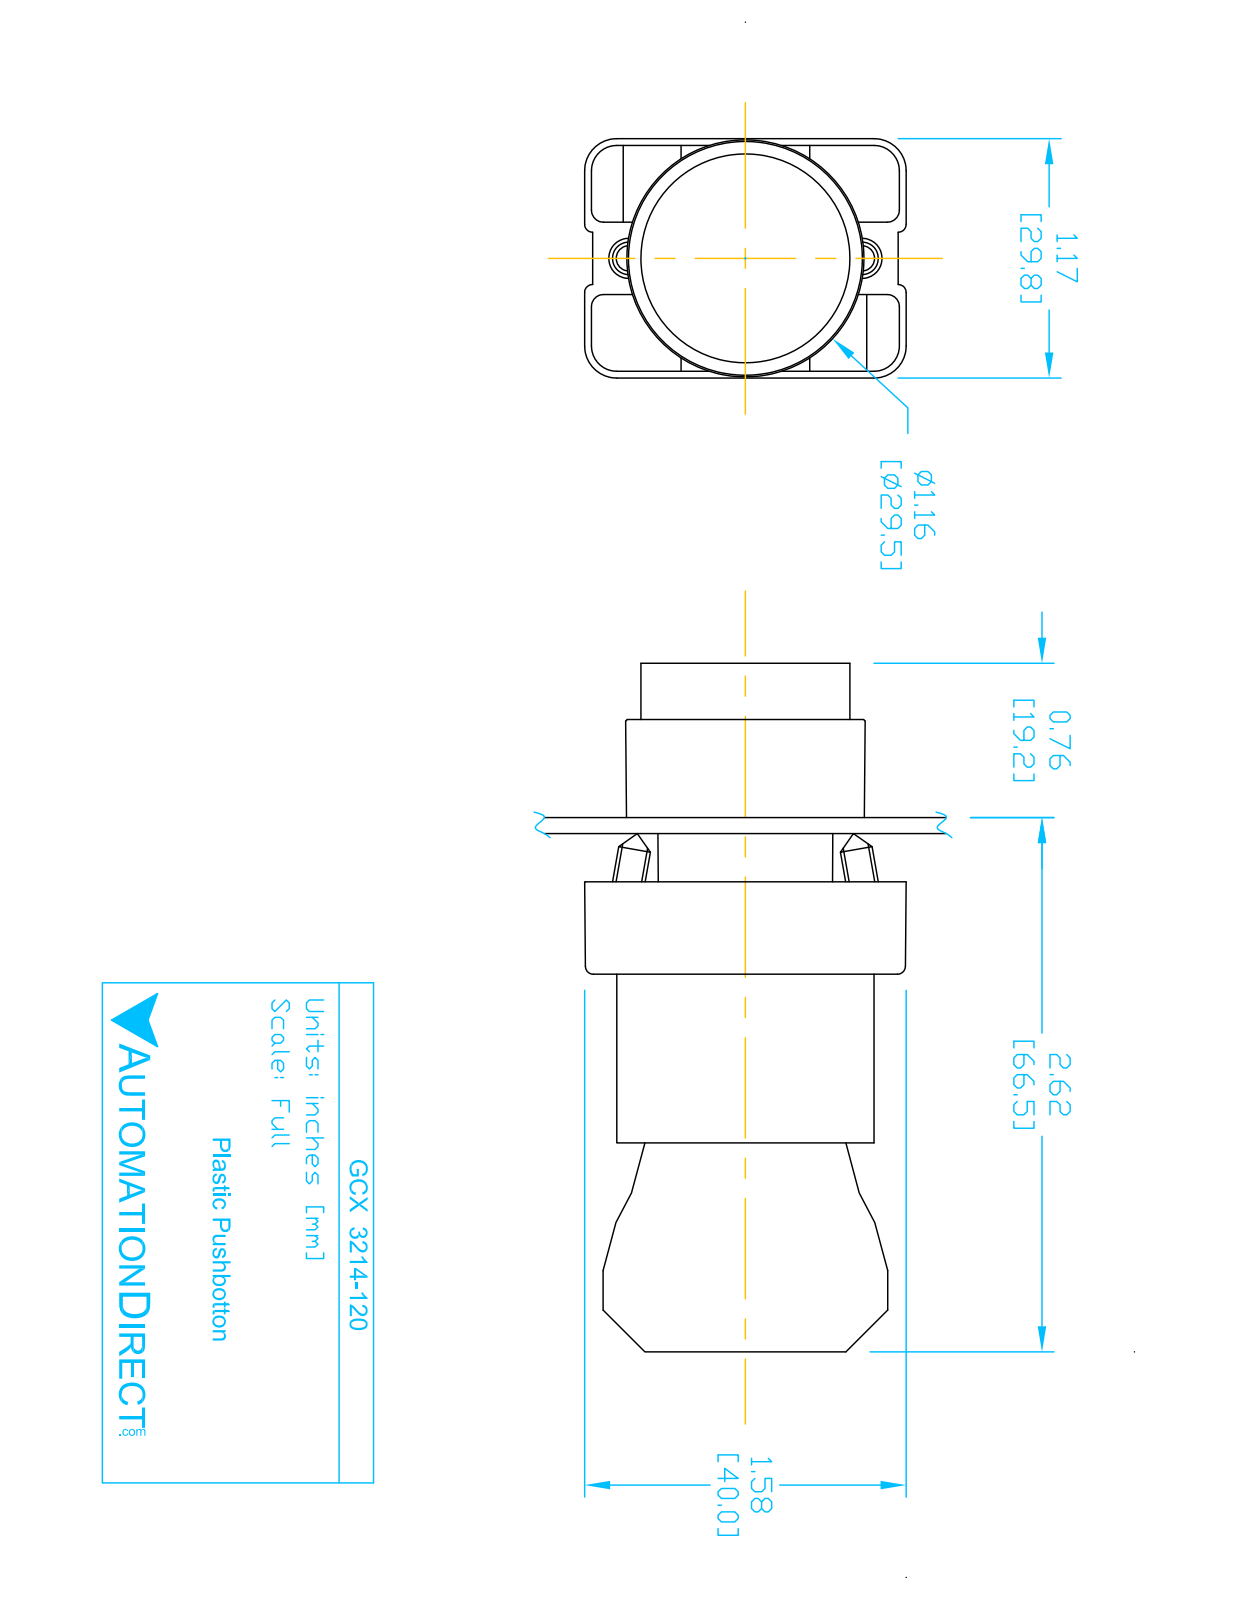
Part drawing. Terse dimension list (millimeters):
name: ECX3029-2; ecx1040; ECX1050; GCX3214-120 (+1 more)
written by: SolidWorks 2016 (AUTOMOTIVE_DESIGN)
unit: mm
bodies: 7 solids, 425 faces (250 planar, 144 cylindrical, 31 other)
size: 84.3 × 40.2 × 29.9
volume: 44 590 mm³; area: 23 430 mm²
holes: 2× ⌀2, 2× ⌀3.1, 2× ⌀3.3, 1× ⌀2.2, 1× ⌀5, 1× ⌀11.9, 1× ⌀22.3, 1× ⌀22.6, 1× ⌀26
bosses: 4× ⌀4, 1× ⌀29.8, 1× ⌀25.5, 1× ⌀24, 1× ⌀21.7, 1× ⌀19.8, 1× ⌀12.8
rounds: 24× R1.5, 12× R1, 12× R3.1, 12× R4, 8× R1, 2× R3.3, 1× R0.5, 1× R1.6
face distances: 21, 14.7, 29.7, 51.3, 30.3, 0.8, 0.8, 14.6, 29.6, 15.1
hole spacings: 6, 13.8, 12, 12.4
